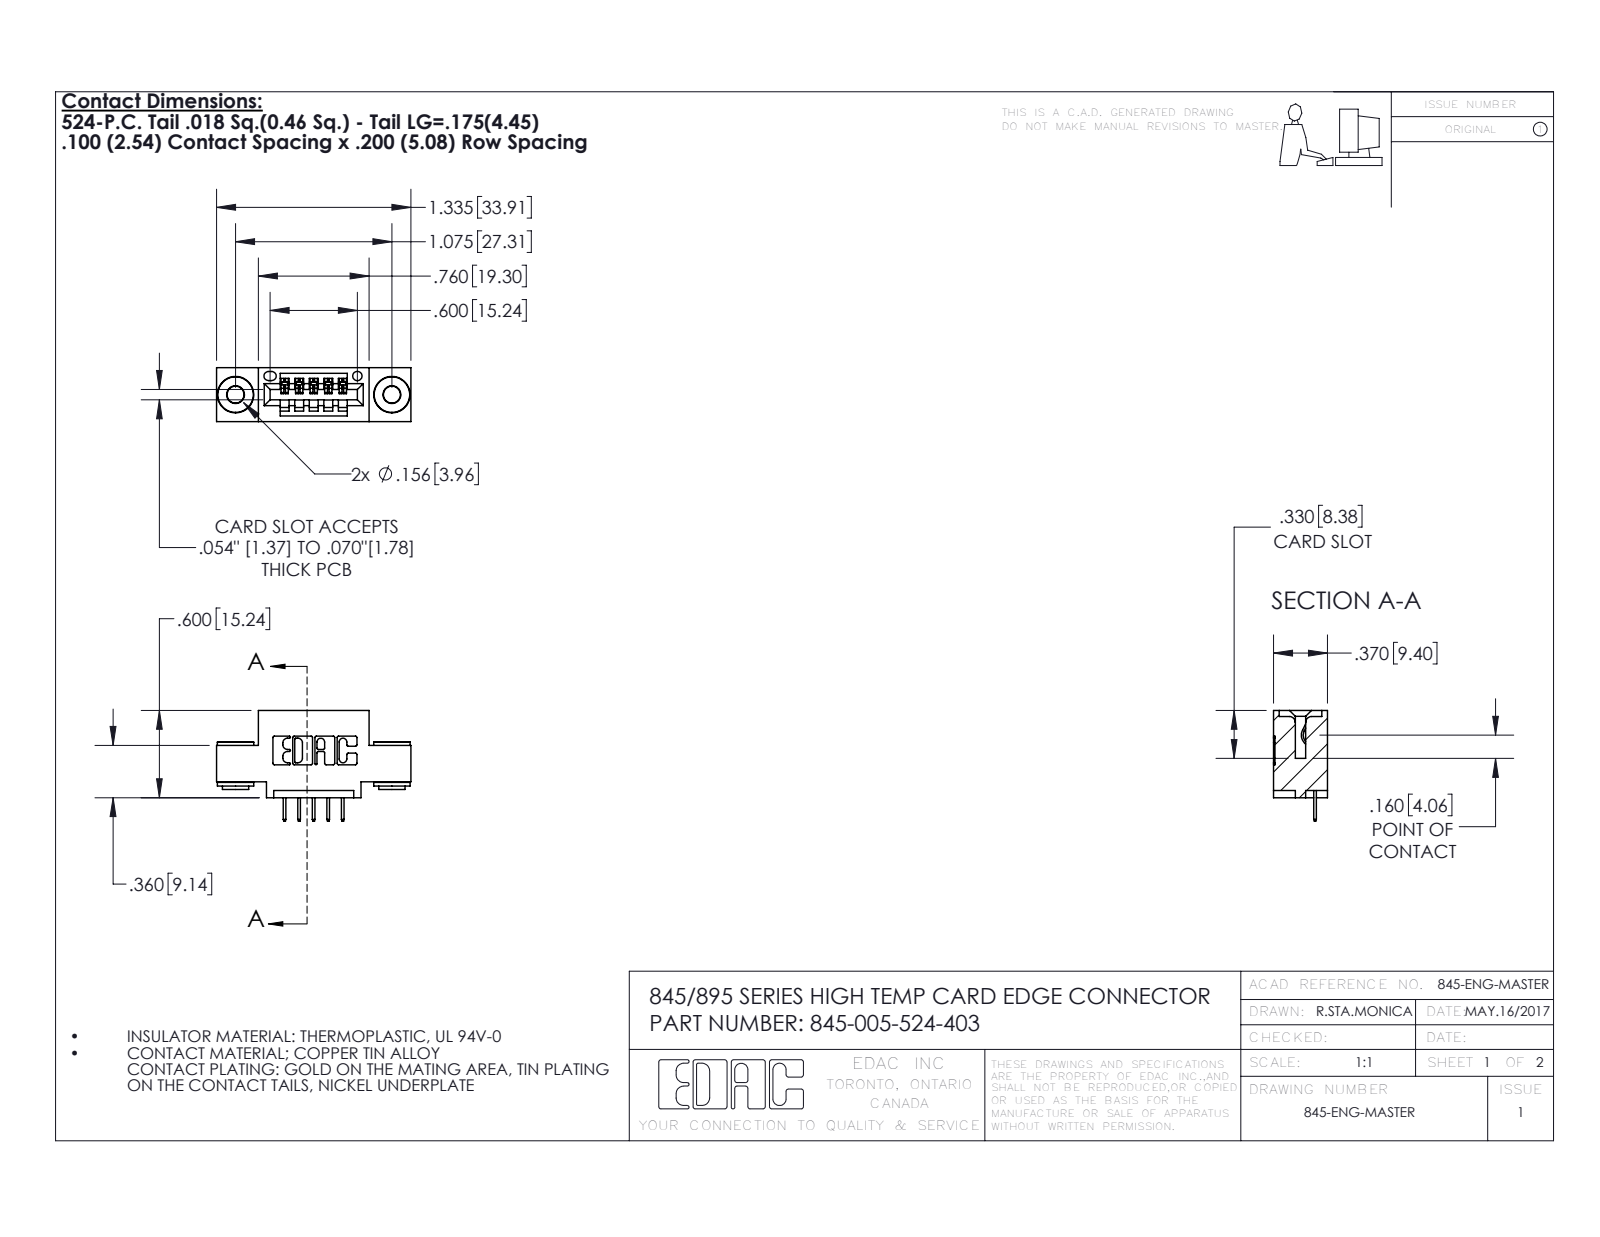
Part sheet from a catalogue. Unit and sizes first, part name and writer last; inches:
Units: inches
Overall size (bounding box): 1.335 × 0.762 × 0.37
Round holes (diameter × count): ⌀0.116 ×2, ⌀0.156 ×2, ⌀0.064 ×1
Round bosses / shafts (diameter × count): ⌀0.25 ×2, ⌀0.18 ×2, ⌀0.136 ×2
Partial cylindrical surfaces — rounded edges, fillets, slot ends (radius × count): R0.01 ×22, R0.006 ×10, R0.007 ×6, R0.031 ×6, R0.026 ×3, R0.031 ×2, R0.04 ×2, R0.014 ×1
Main face-to-face distances: 0.37, 0.2, 0.1, 0.072, 0.298, 0.025, 0.25, 0.06, 0.16, 0.55
Hole centre spacings: 0.27, 0.847, 1.075
Volume: 0.174 in³ · Surface area: 5.44 in²
Bodies: 8 solids, 478 faces (324 planar, 146 cylindrical, 8 other)
Part name (STEP PRODUCT): 345-005-524-403; 345-292-001_345-293-124; 345 Part_0.110 Offset - 0.156 Dia-TH; 345-250-002_345-250-002-102
STEP written by: SolidWorks 2016 (CONFIG_CONTROL_DESIGN)
